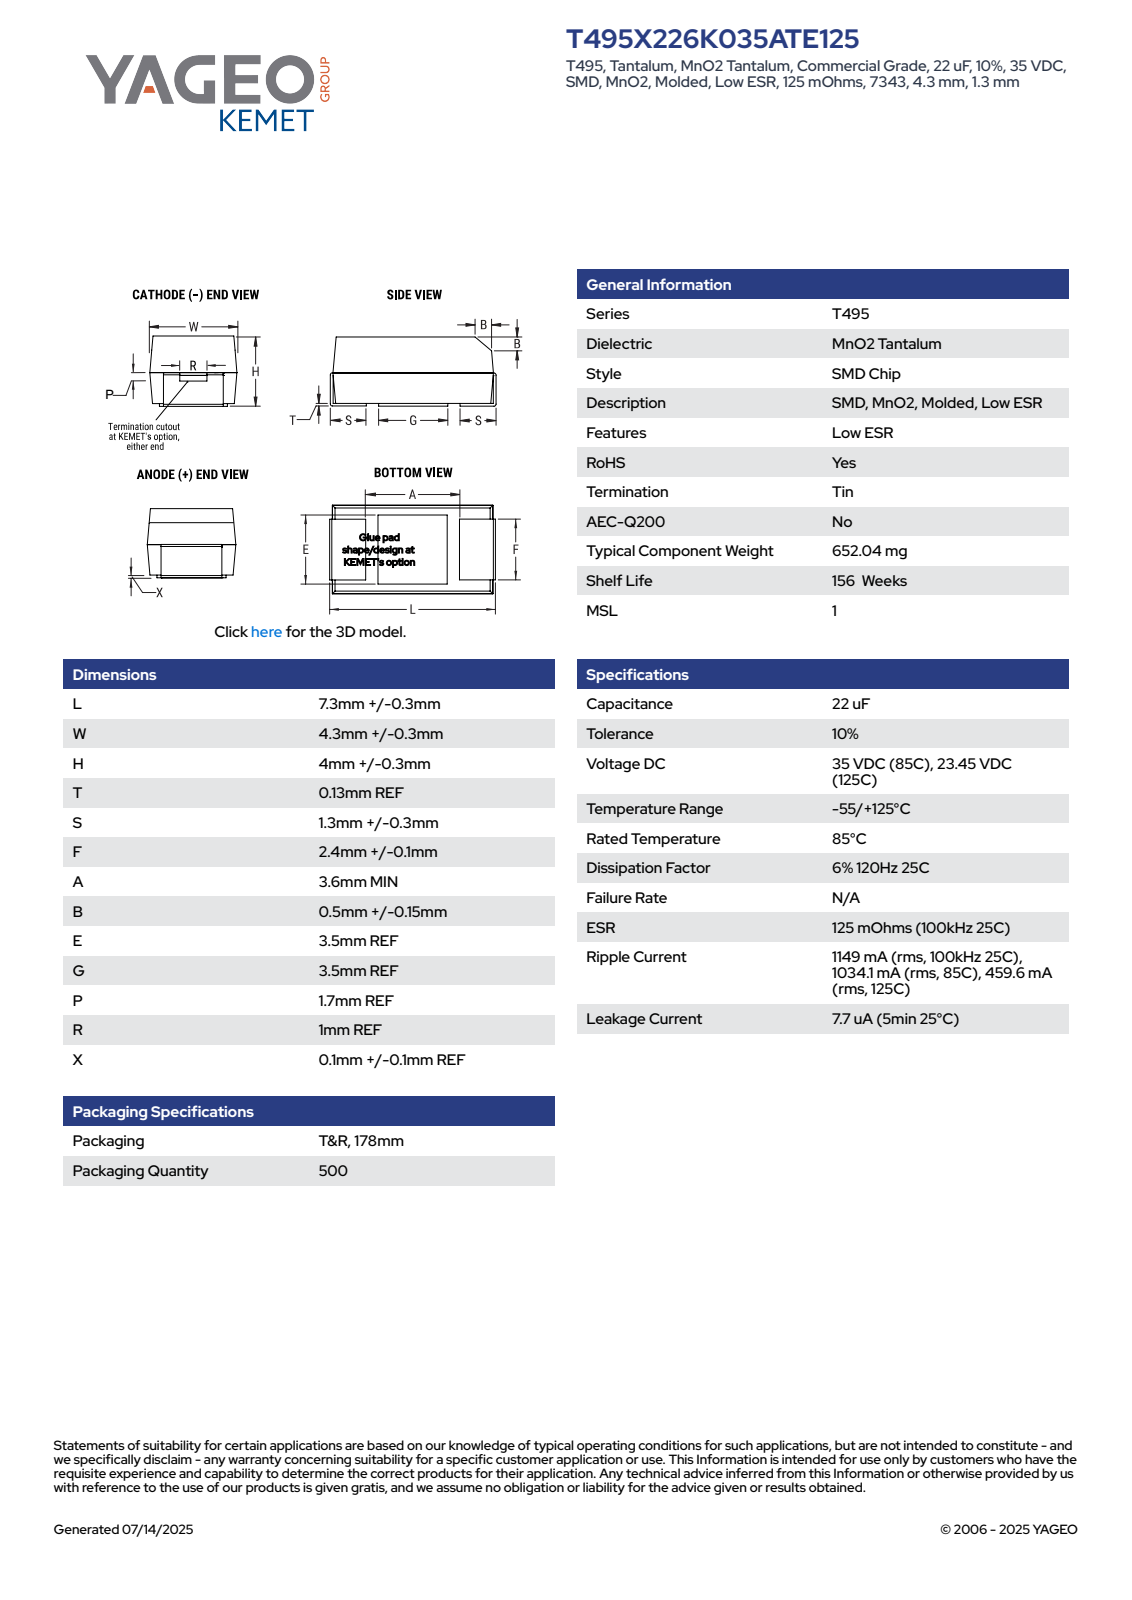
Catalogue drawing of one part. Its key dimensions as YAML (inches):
part_name: "CTSM_TCM2NK_7343_L7.6W4.6H4.3T0.13S1.3F2.5A3.6B0.65E3.5G3.5P1.7R1X0.2"
step_written_by: "SolidWorks 2020 (AUTOMOTIVE_DESIGN)"
units: inches
bodies: {solids: 4, faces: 100, planar: 95, cylindrical: 5, other: 0}
overall_size: [0.299, 0.181, 0.169]
volume: 0.008
surface_area: 0.288
partial_cylinders:
  - {radius: 0.004, count: 4}
face_to_face_distances: [0.18, 0.169, 0.161, 0.294, 0.164, 0.299, 0.289, 0.081, 0.219, 0.076]
